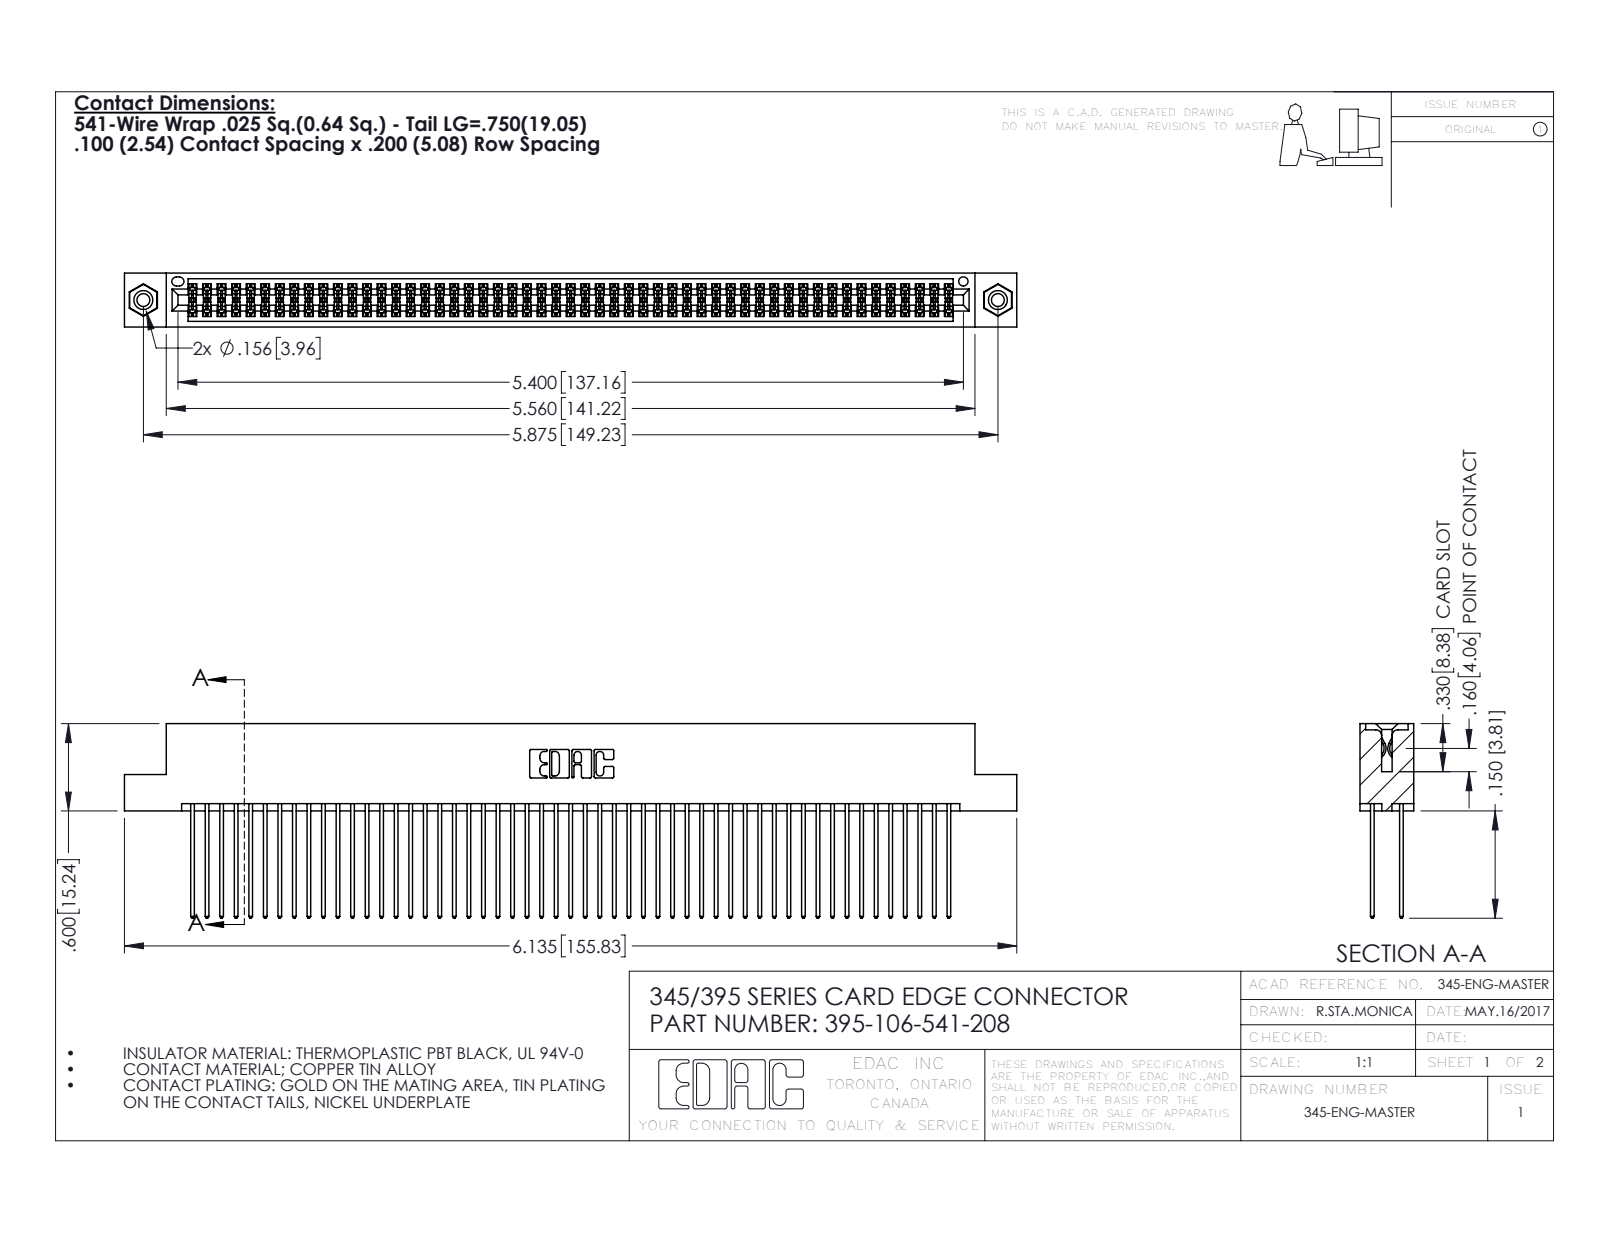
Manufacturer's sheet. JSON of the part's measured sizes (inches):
{"part_name": "395-106-541-208; 345-292-001_345-293-141; 345 Part_Flush Mounting Lugs - 0.156 Dia-TI; 345-250-001_345-250-003-102", "step_written_by": "SolidWorks 2016 (CONFIG_CONTROL_DESIGN)", "units": "inches", "bodies": {"solids": 109, "faces": 5486, "planar": 3610, "cylindrical": 1860, "other": 16}, "overall_size": [6.135, 1.337, 0.37], "volume_in3": 0.967, "surface_area_in2": 41.08, "round_holes": [[0.089, 2], [0.125, 2], [0.156, 2], [0.064, 1]], "round_bosses_or_shafts": [[0.155, 2]], "partial_cylinders_radius": [[0.006, 159], [0.01, 106], [0.01, 22], [0.007, 6], [0.031, 6], [0.026, 3], [0.014, 2], [0.019, 2]], "face_to_face_distances": [0.072, 0.298, 0.2, 0.098, 0.272, 0.025, 0.225, 0.37, 0.175, 0.149], "hole_center_spacings": [0.27, 5.639, 5.875]}
